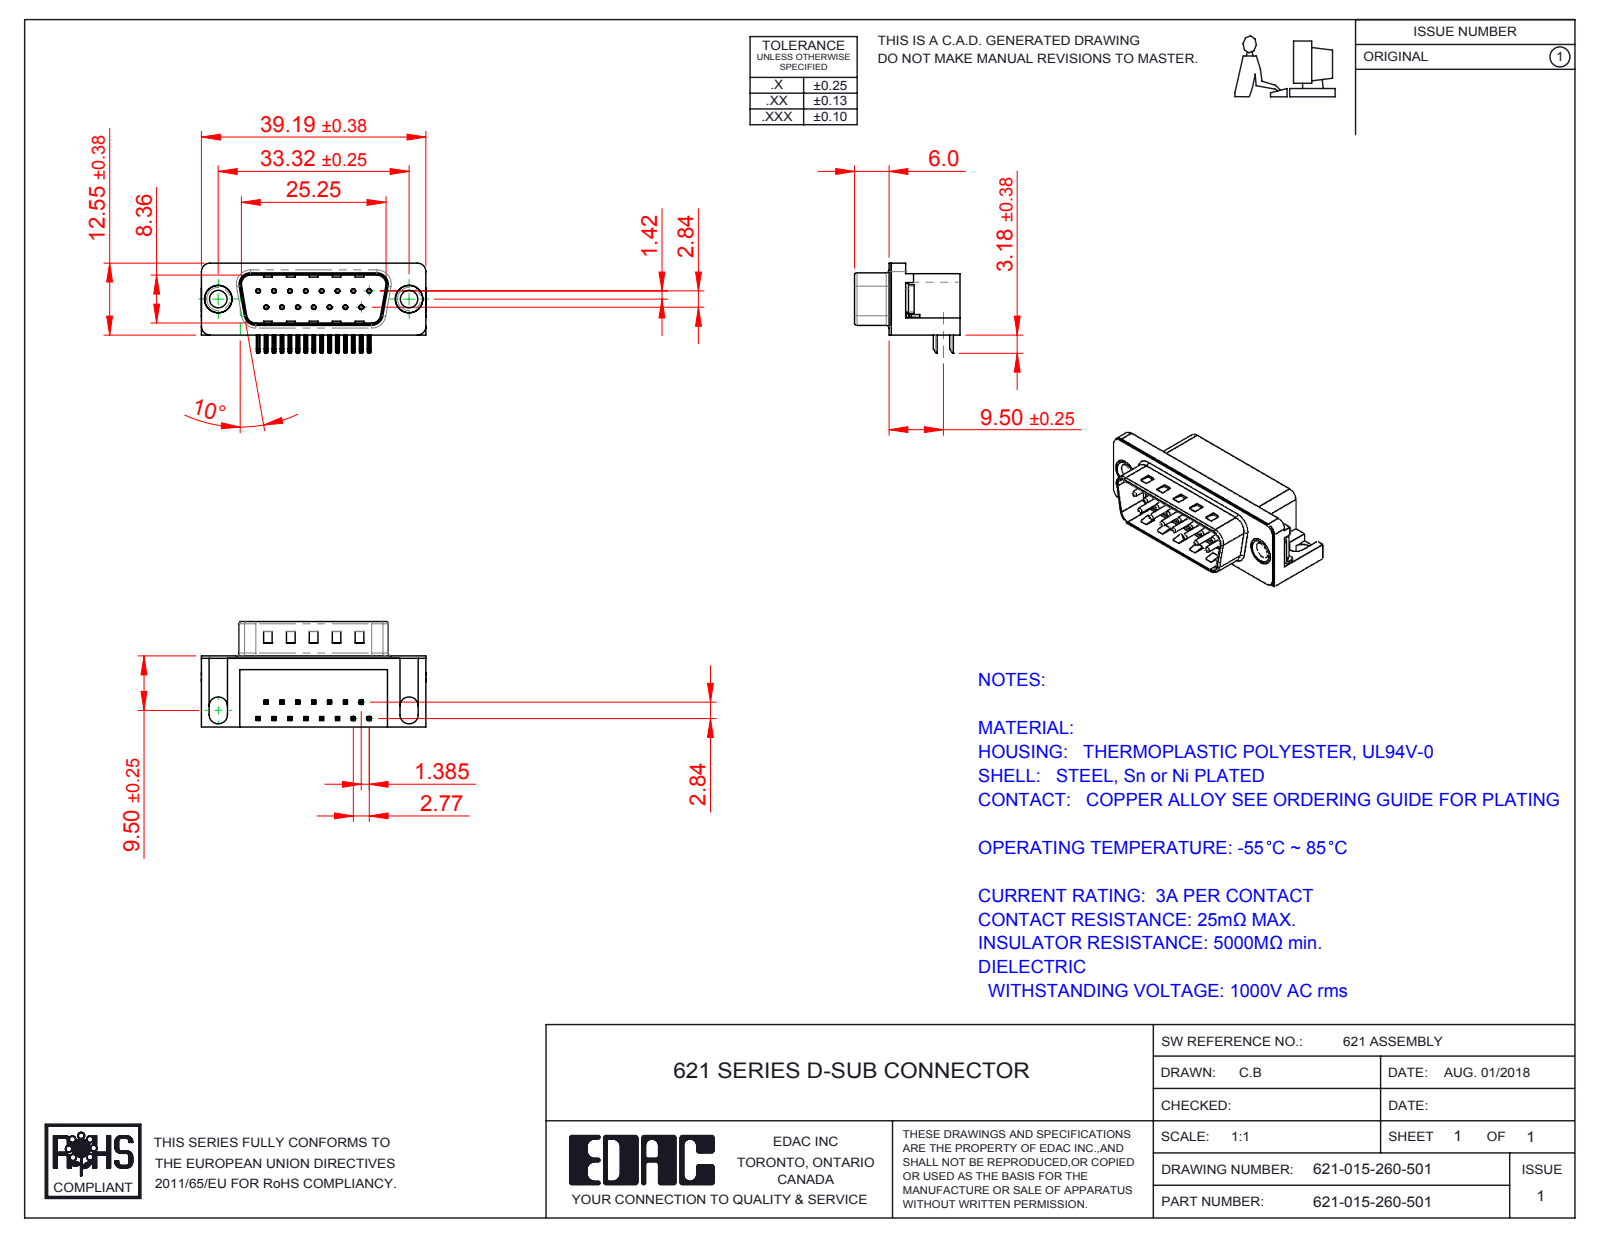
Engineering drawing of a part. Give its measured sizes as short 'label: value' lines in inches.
name: 621 Housing_15 Socket; 621 Non Board Mount; 621 Shell_15 Socket; 621 Thru Hole Rivet (+3 more)
written by: SolidWorks 2016 (CONFIG_CONTROL_DESIGN)
unit: in
bodies: 21 solids, 1431 faces (891 planar, 423 cylindrical, 117 other)
size: 1.544 × 0.724 × 0.619
volume: 0.266 in³; area: 8.454 in²
holes: 15× ⌀0.014, 15× ⌀0.031, 2× ⌀0.12, 2× ⌀0.157, 2× ⌀0.189, 2× ⌀0.197
bosses: 15× ⌀0.03, 2× ⌀0.193, 2× ⌀0.187, 2× ⌀0.152
rounds: 68× R0.01, 30× R0.005, 16× R0.039, 9× R0.02, 8× R0.063, 6× R0.059, 4× R0.035, 4× R0.079
face distances: 0.016, 0.472, 0.407, 0.083, 0.488, 0.412, 0.067, 0.428, 0.345, 0.114
hole spacings: 0.124, 0.109, 0.218, 0.327, 0.436, 0.198, 0.198, 0.294
